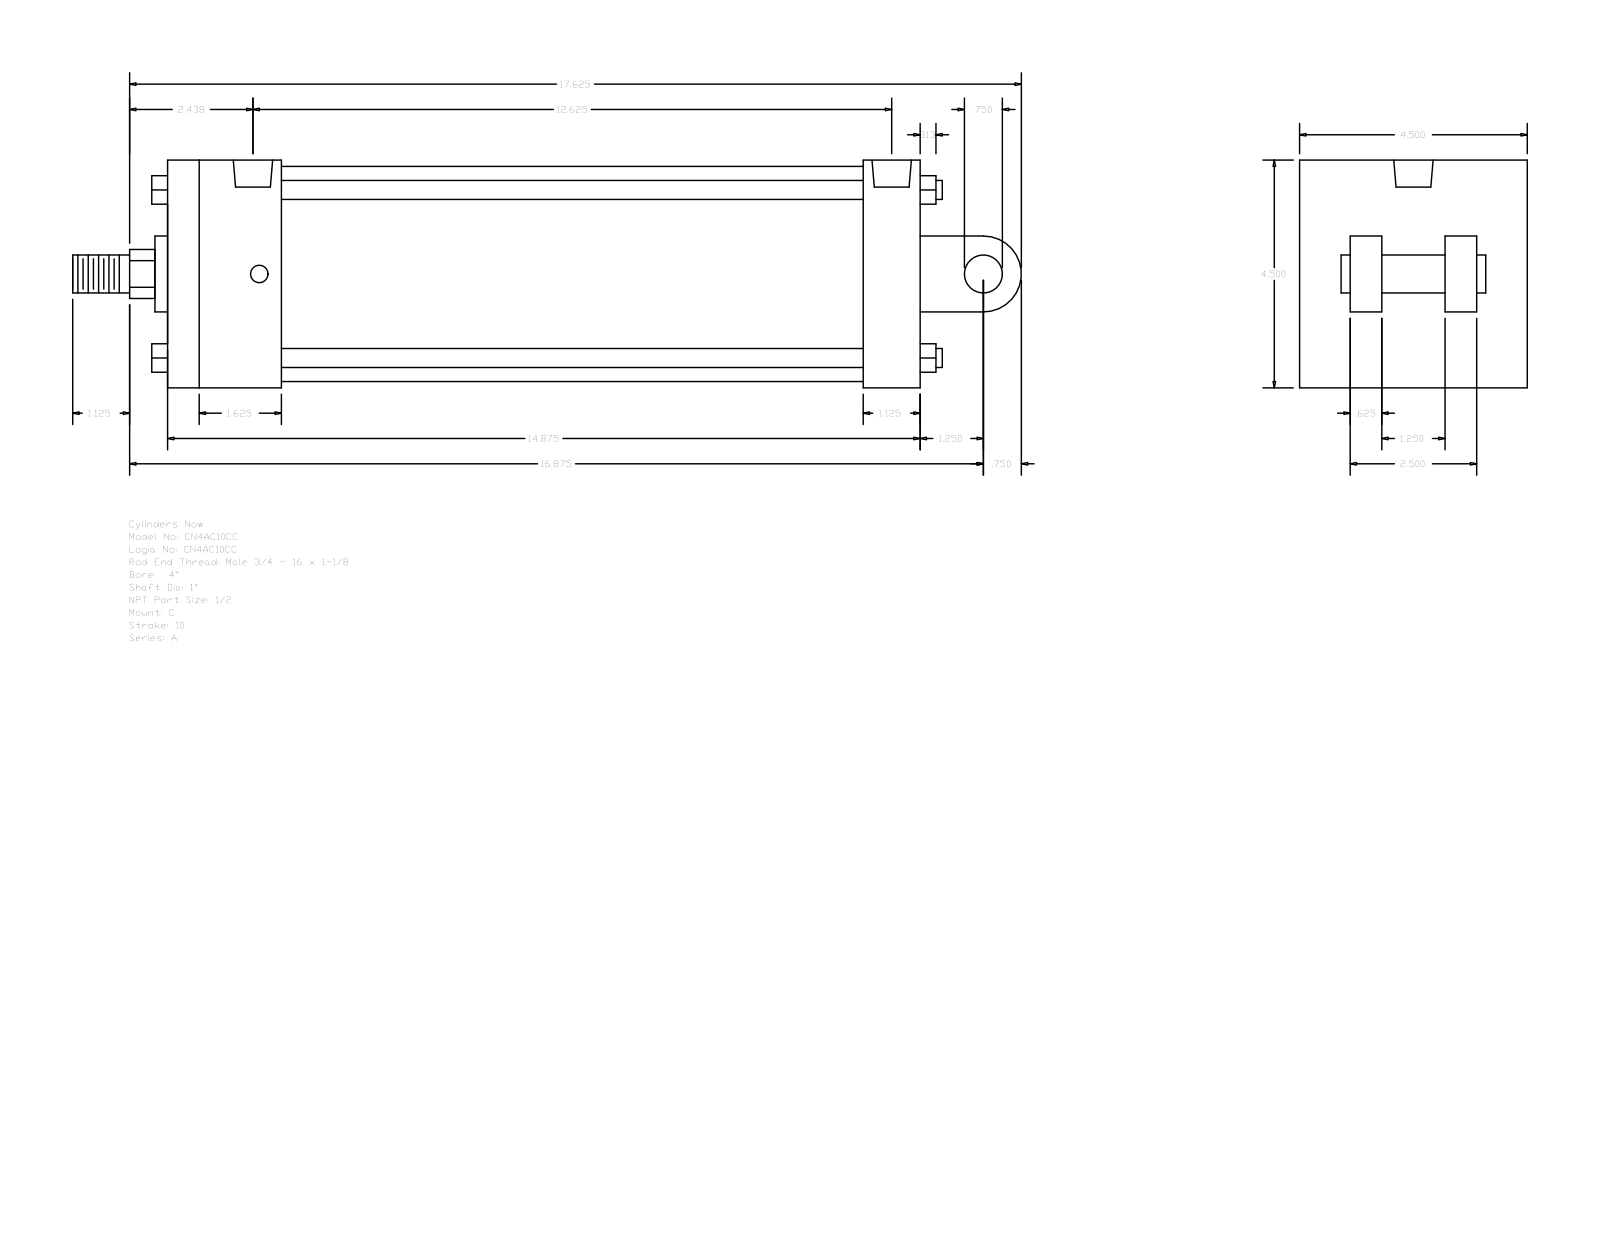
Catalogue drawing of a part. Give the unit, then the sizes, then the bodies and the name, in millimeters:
Units: millimetres
Overall size (bounding box): 476.25 × 114.3 × 114.3
Round holes (diameter × count): ⌀8.73 ×4, ⌀19.77 ×2
Round bosses / shafts (diameter × count): ⌀9.53 ×4, ⌀19.05 ×2, ⌀107.95 ×1, ⌀38.1 ×1, ⌀25.4 ×1
Partial cylindrical surfaces — rounded edges, fillets, slot ends (radius × count): R12.29 ×1, R19.05 ×1
Main face-to-face distances: 114.3, 377.83, 73.03, 349.25, 28.58, 57.15, 292.1, 320.68, 41.27, 38.1
Hole centre spacings: 3.18, 314.32, 317.5, 320.68
Bodies: 0 solids, 135 faces (102 planar, 33 cylindrical, 0 other)
Part name (STEP PRODUCT): A_C__0400_1
STEP written by: GSSL Pune (CONFIG_CONTROL_DESIGN)
